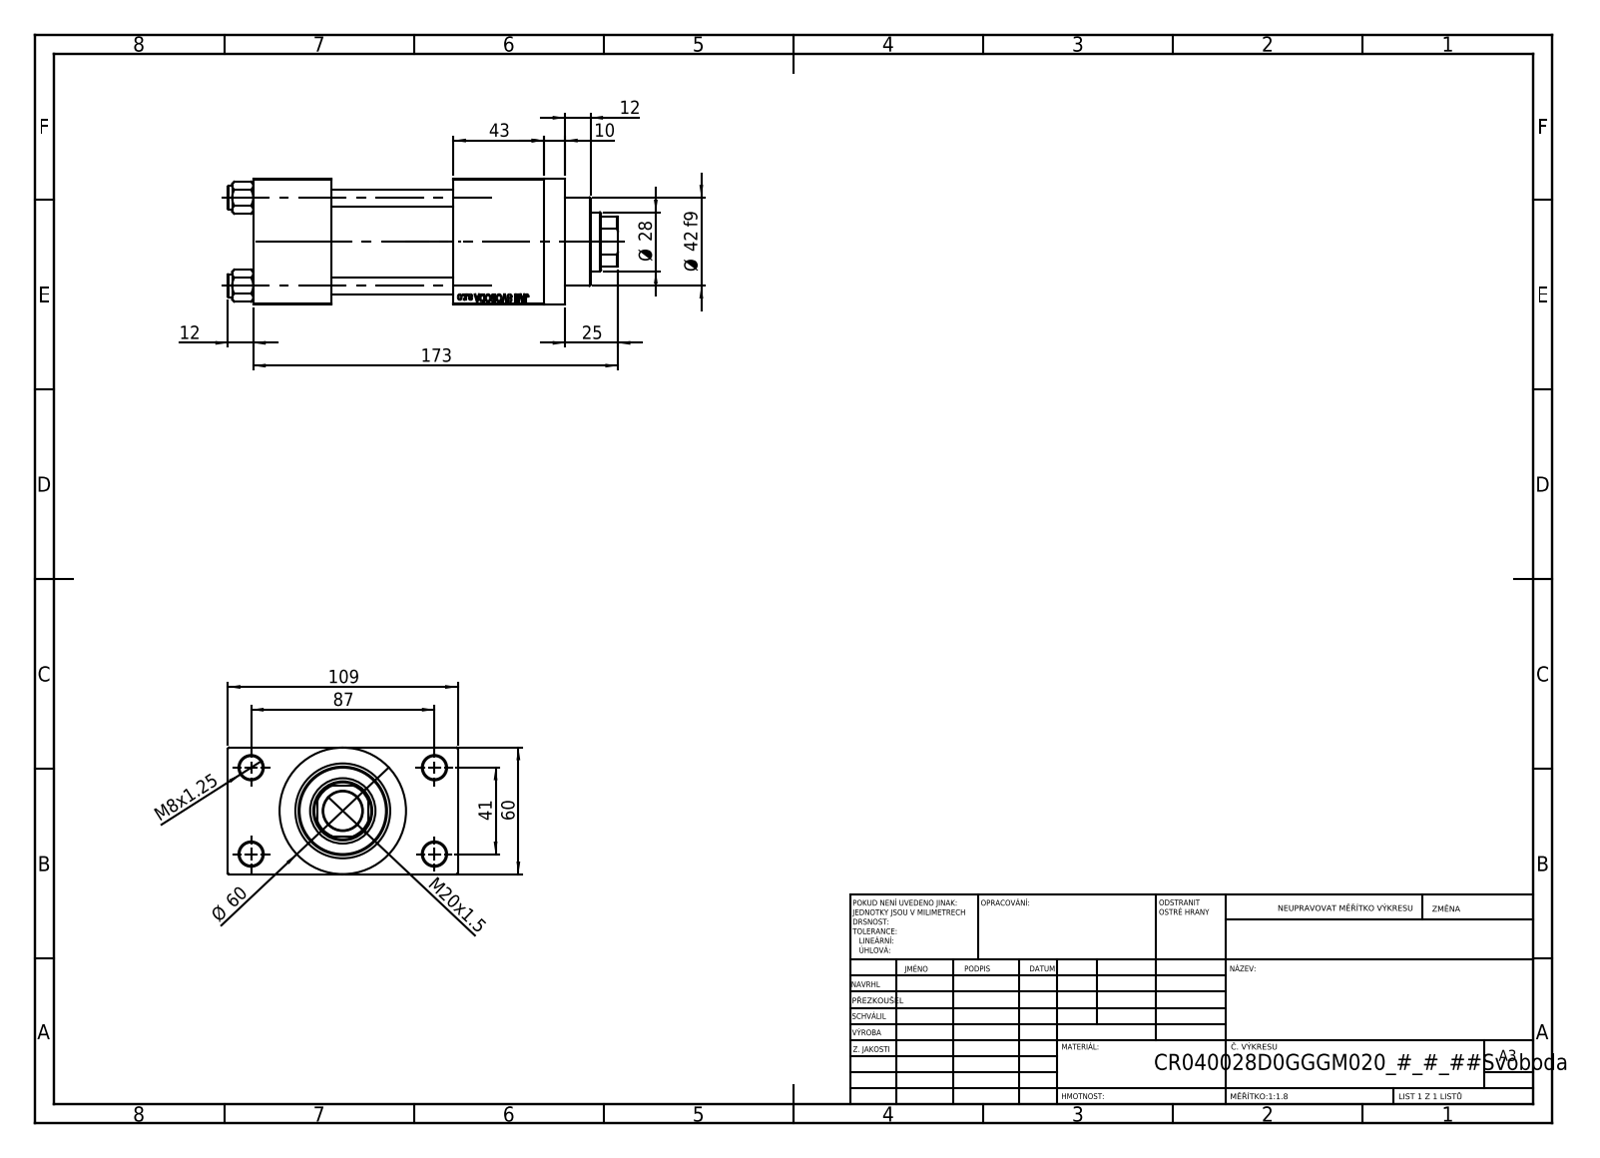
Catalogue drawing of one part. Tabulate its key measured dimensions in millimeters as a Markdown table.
| quantity | value |
| --- | --- |
| part name | V215CR_D_Body; V215CR_D_TYCINKA; NUT_M5_D; V215CR_VCP_D (+1 more) |
| STEP written by | SolidWorks 2019 (CONFIG_CONTROL_DESIGN) |
| units | millimeters |
| bodies | 11 solids, 1105 faces (498 planar, 89 cylindrical, 518 other) |
| overall size | 185 × 109 × 60 |
| volume | 534 120 mm³ |
| surface area | 127 827 mm² |
| round holes (diameter × count) | 8 × 4, 11 × 4, 7 × 2, 16.66 × 2, 24 × 2, 18.5 × 1, 28 × 1, 31 × 1, 40 × 1, 45 × 1 |
| round bosses / shafts (diameter × count) | 11 × 4, 60 × 1, 46 × 1, 42 × 1 |
| partial cylindrical surfaces (radius × count) | 13.5 × 1 |
| main face-to-face distances | 60, 84.5, 24.5, 58, 37, 95, 138, 101, 43, 109 |
| hole center spacings | 22.65, 29.49, 41.7, 47.15, 48.09, 64.35, 76.49, 41 |
